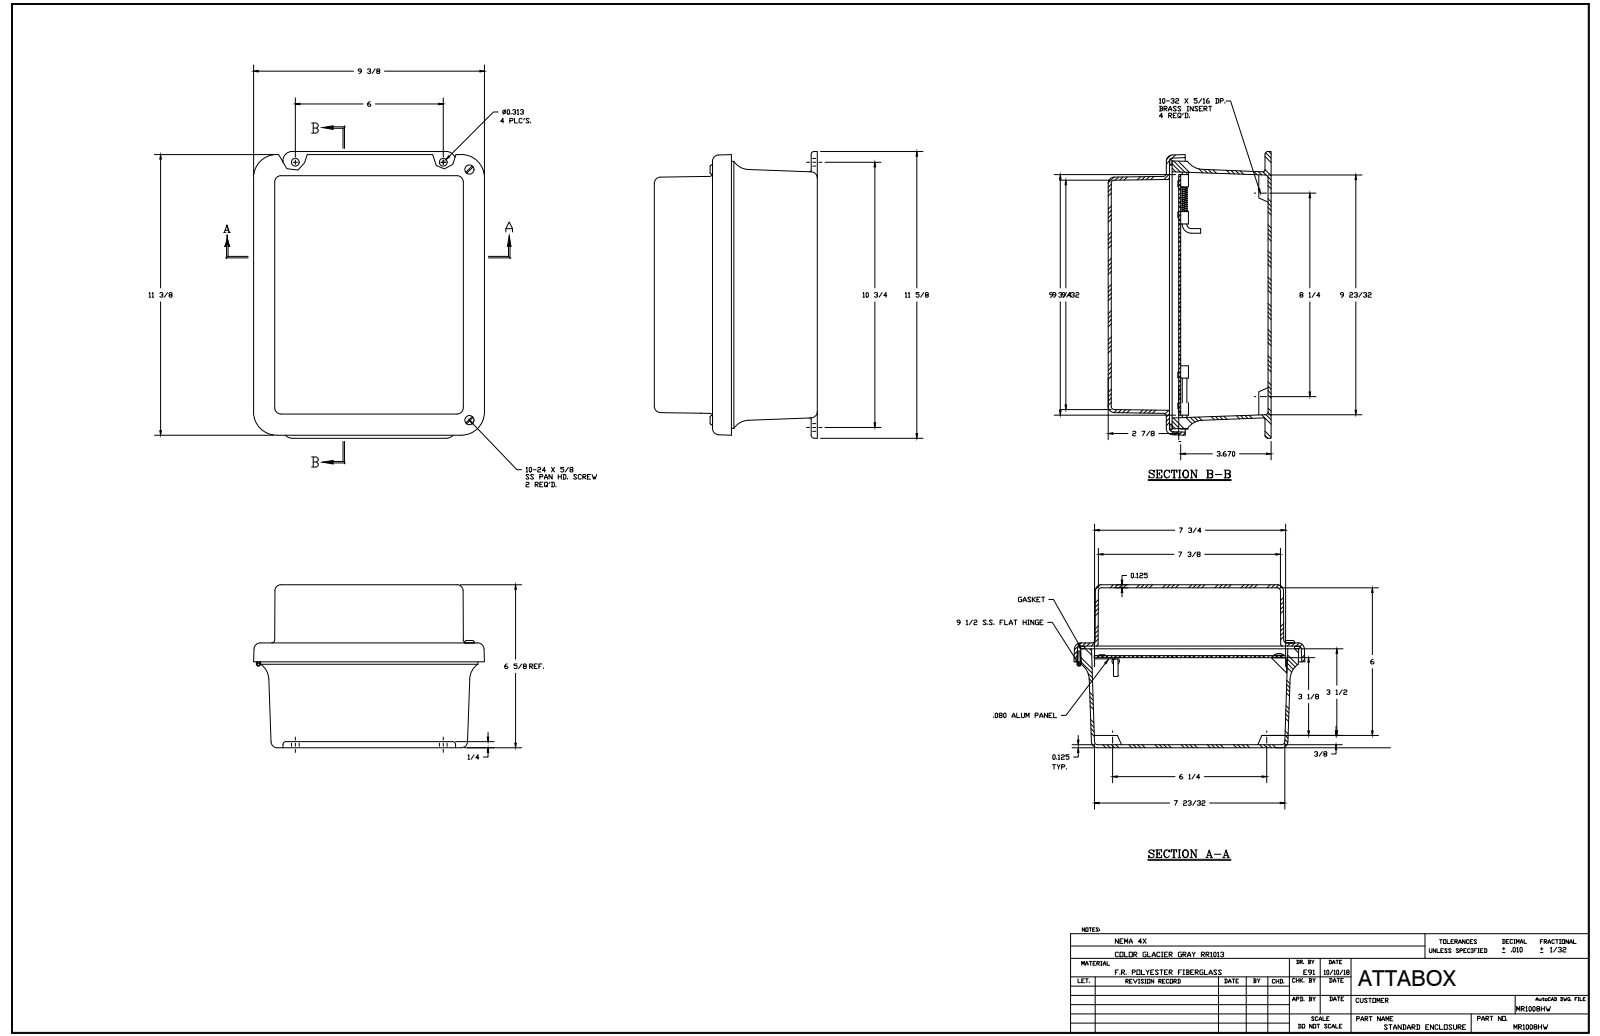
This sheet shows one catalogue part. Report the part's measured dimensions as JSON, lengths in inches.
{"part_name": "MR1008HW", "step_written_by": "SolidWorks 2018 (AUTOMOTIVE_DESIGN)", "units": "inches", "bodies": {"solids": 22, "faces": 801, "planar": 269, "cylindrical": 303, "other": 229}, "overall_size": [11.625, 9.393, 6.594], "volume_in3": 68.41, "surface_area_in2": 954.5, "round_holes": [[0.131, 8], [0.14, 8], [0.152, 5], [0.156, 4], [0.218, 4], [0.145, 2], [0.085, 1], [0.085, 1]], "round_bosses_or_shafts": [[0.25, 8], [0.27, 6], [0.125, 5], [0.125, 3], [0.19, 2], [0.156, 2], [0.155, 1], [0.155, 1]], "partial_cylinders_radius": [[0.125, 24], [0.031, 20], [0.25, 12], [0.2, 4], [0.375, 4], [0.75, 4], [0.063, 2]], "face_to_face_distances": [0.125, 0.125, 6.344, 6.469, 6.594, 6.469, 4.109, 3.984, 2.36, 2.485], "hole_center_spacings": [6, 3, 0.25, 1.337, 2.5, 2.75, 7.251, 9.25]}
